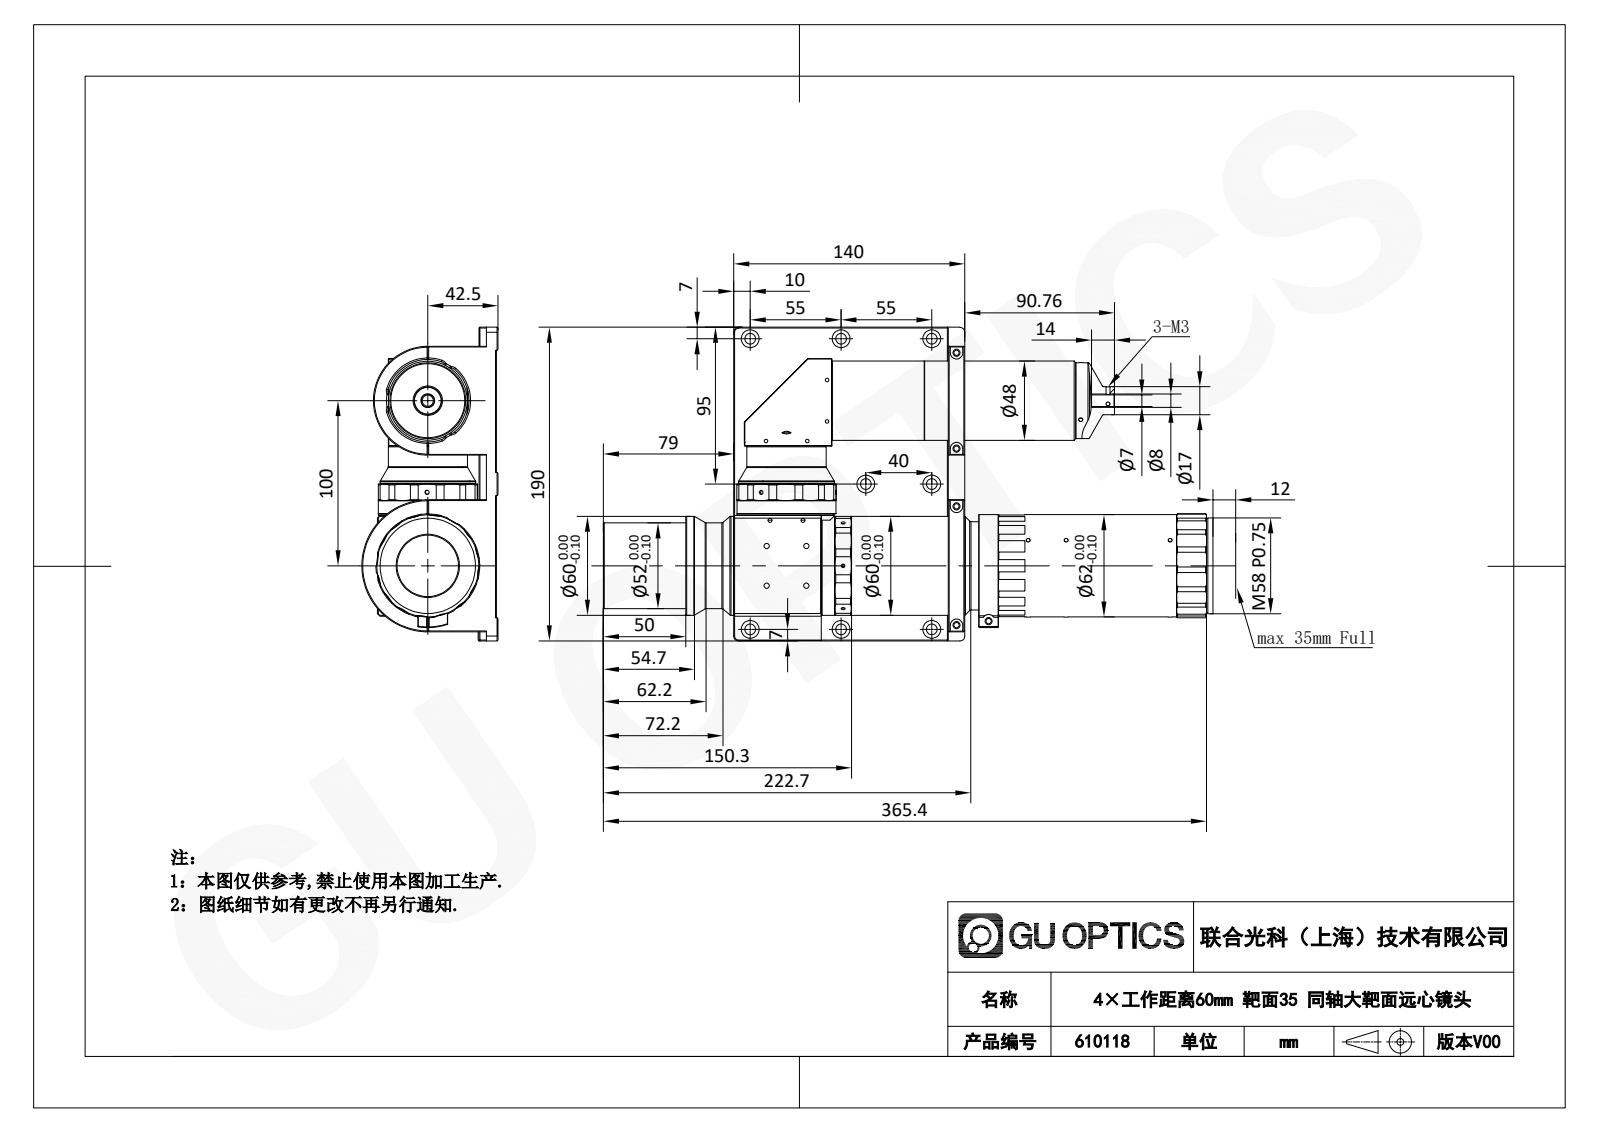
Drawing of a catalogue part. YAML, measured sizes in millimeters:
part_name: "DTCA35F-11C-G-M58-ALV3(8),"
step_written_by: "SolidWorks 2017 (CONFIG_CONTROL_DESIGN)"
units: millimeters
bodies: {solids: 6, faces: 1424, planar: 421, cylindrical: 554, other: 449}
overall_size: [369.4, 190, 82.53]
volume: 1728000
surface_area: 234126
round_holes:
  - {diameter: 2.5, count: 22}
  - {diameter: 3.3, count: 19}
  - {diameter: 4.5, count: 16}
  - {diameter: 2.4, count: 13}
  - {diameter: 7.5, count: 11}
  - {diameter: 6.5, count: 8}
  - {diameter: 11, count: 8}
  - {diameter: 3.2, count: 4}
  - {diameter: 6, count: 4}
  - {diameter: 1.5, count: 2}
  - {diameter: 2.2, count: 2}
  - {diameter: 3.4, count: 1}
round_bosses_or_shafts:
  - {diameter: 60, count: 2}
  - {diameter: 58, count: 2}
  - {diameter: 48, count: 2}
  - {diameter: 62, count: 1}
  - {diameter: 57.97, count: 1}
  - {diameter: 57, count: 1}
  - {diameter: 56.8, count: 1}
  - {diameter: 53.5, count: 1}
partial_cylinders:
  - {radius: 15, count: 32}
  - {radius: 2, count: 16}
  - {radius: 3, count: 10}
  - {radius: 5, count: 6}
  - {radius: 3.75, count: 4}
  - {radius: 1, count: 2}
  - {radius: 21, count: 2}
  - {radius: 30.5, count: 2}
face_to_face_distances: [10.5, 11.5, 1, 72, 10, 61.5, 6.5, 73, 130, 140]
hole_center_spacings: [24, 40, 5, 6, 33.94, 41.4, 41.7, 45]
